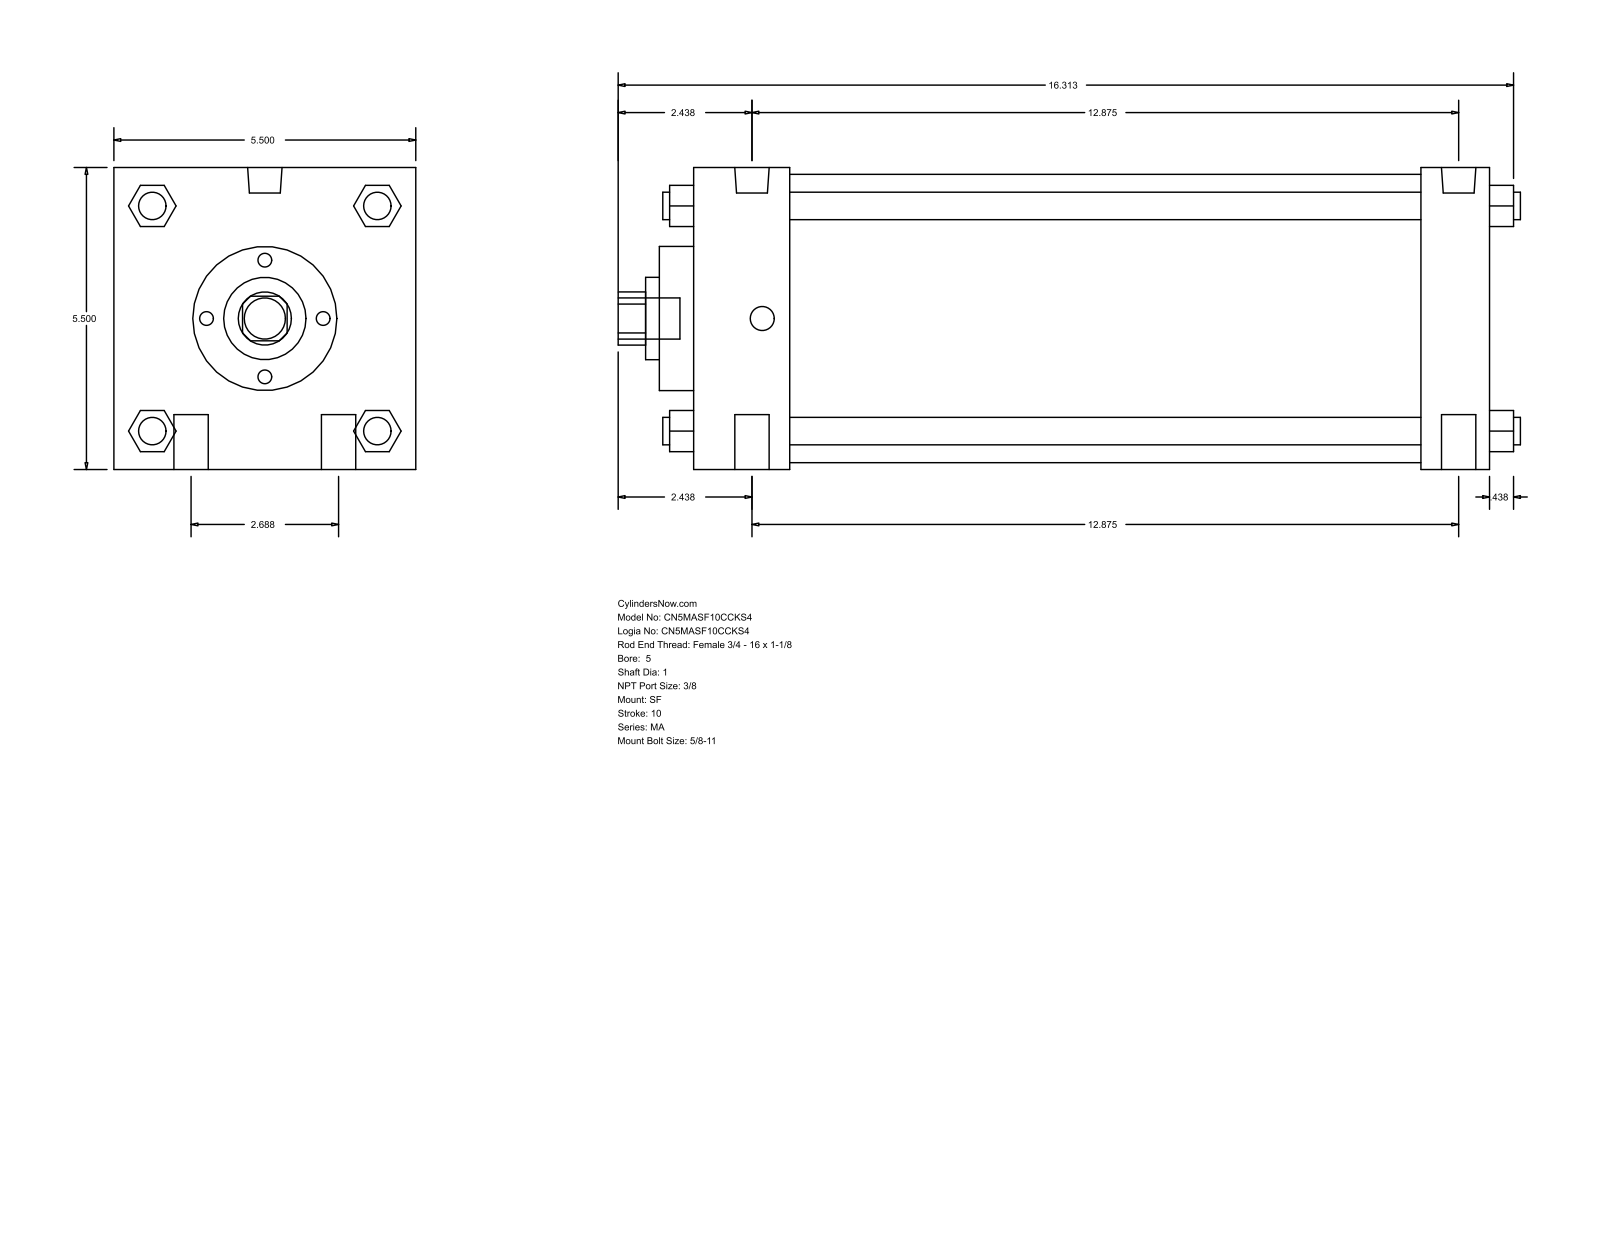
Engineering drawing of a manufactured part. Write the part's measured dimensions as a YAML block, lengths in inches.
part_name: "MA_SF__0500_1"
step_written_by: "GSSL Pune (CONFIG_CONTROL_DESIGN)"
units: inches
bodies: {solids: 0, faces: 126, planar: 95, cylindrical: 31, other: 0}
overall_size: [16.437, 5.5, 5.5]
round_holes:
  - {diameter: 1, count: 1}
  - {diameter: 1.5, count: 1}
  - {diameter: 2.625, count: 1}
  - {diameter: 5.25, count: 1}
round_bosses_or_shafts:
  - {diameter: 0.625, count: 4}
  - {diameter: 0.5, count: 4}
  - {diameter: 0.627, count: 2}
  - {diameter: 0.437, count: 2}
  - {diameter: 0.75, count: 1}
partial_cylinders:
  - {radius: 0.484, count: 1}
face_to_face_distances: [5.5, 14.5, 1.75, 13.25, 11.5, 12.75, 1.25, 0.625, 2.375, 13.875]
